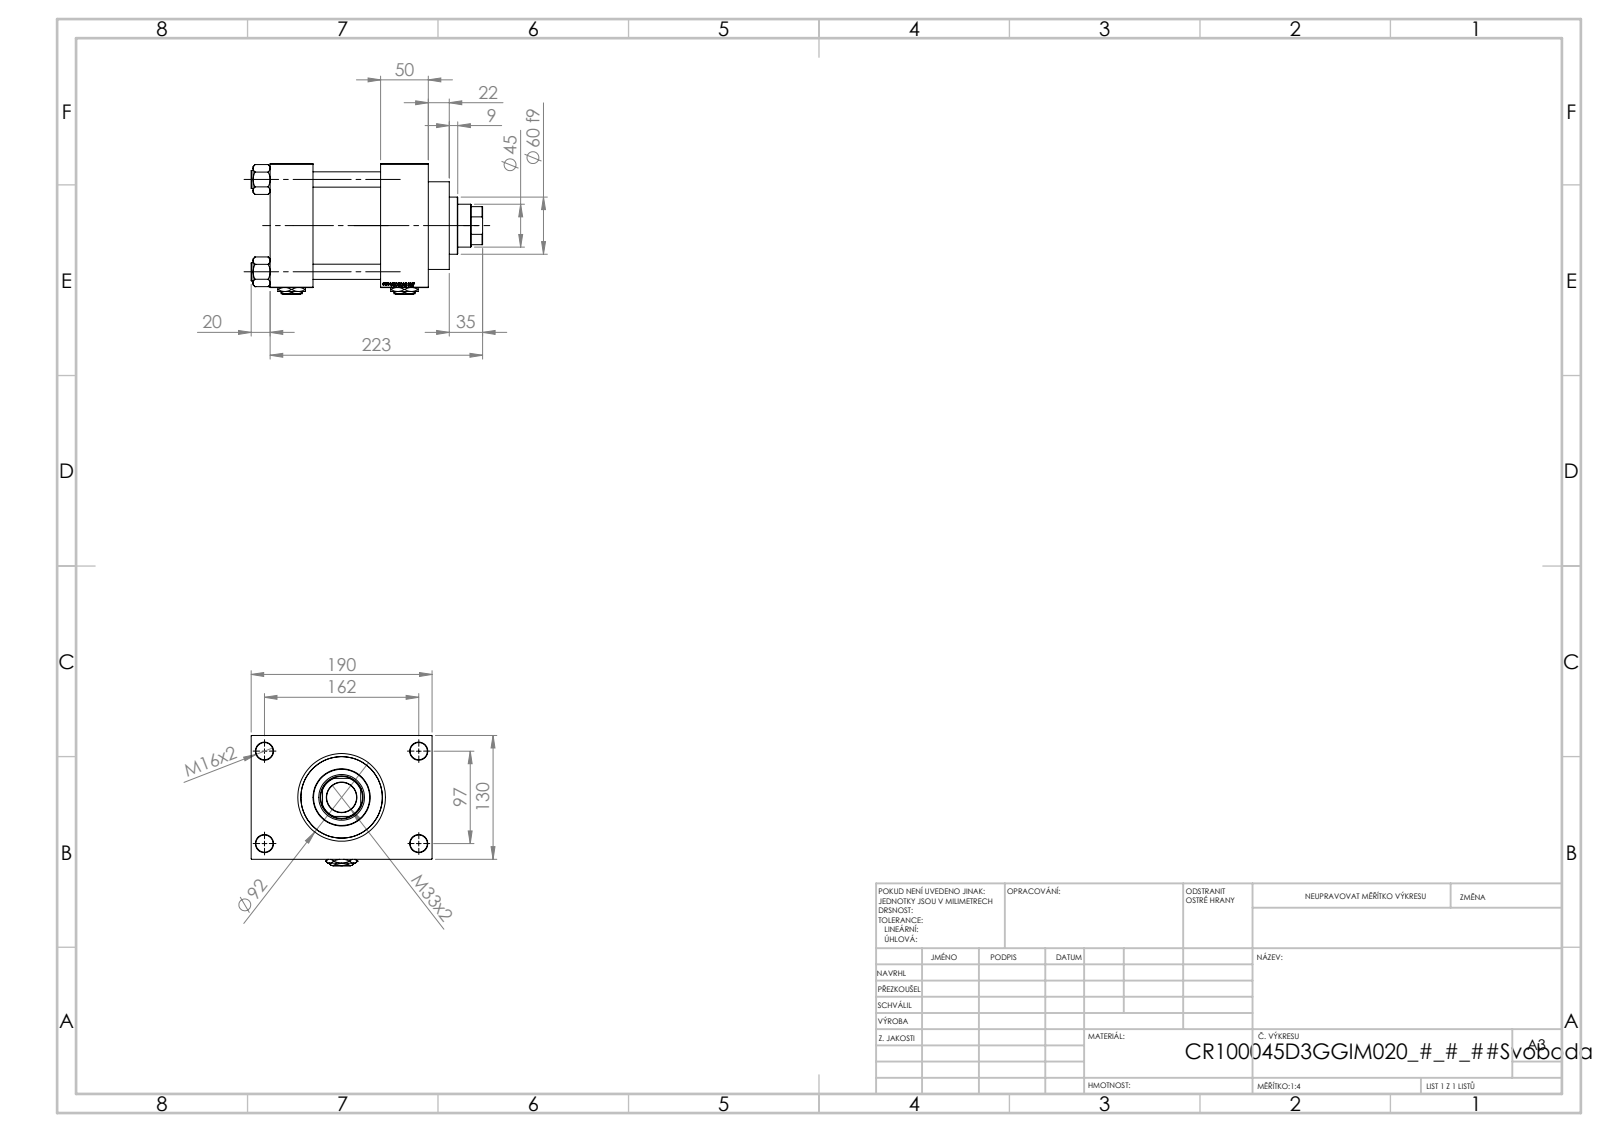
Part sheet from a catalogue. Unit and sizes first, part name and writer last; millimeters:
Units: millimetres
Overall size (bounding box): 243 × 190 × 137
Round holes (diameter × count): ⌀16 ×4, ⌀18 ×4, ⌀7 ×2, ⌀26.44 ×2, ⌀35 ×2, ⌀31.5 ×1, ⌀45 ×1, ⌀48 ×1, ⌀76 ×1, ⌀85.5 ×1, ⌀100 ×1
Round bosses / shafts (diameter × count): ⌀19 ×4, ⌀106 ×1, ⌀92 ×1, ⌀60 ×1
Partial cylindrical surfaces — rounded edges, fillets, slot ends (radius × count): R22 ×1
Main face-to-face distances: 130, 45, 116, 71, 166, 121, 50, 160, 30, 20
Hole centre spacings: 32.55, 68.52, 94.41, 96.9, 102.27, 129.45, 161.73, 97
Volume: 2 592 000 mm³ · Surface area: 359 312 mm²
Bodies: 13 solids, 1253 faces (593 planar, 100 cylindrical, 560 other)
Part name (STEP PRODUCT): V215CR_D_Body; NUT_M5_D; V215CR_D_TYCINKA; V215_VC_A (+2 more)
STEP written by: SolidWorks 2019 (CONFIG_CONTROL_DESIGN)
